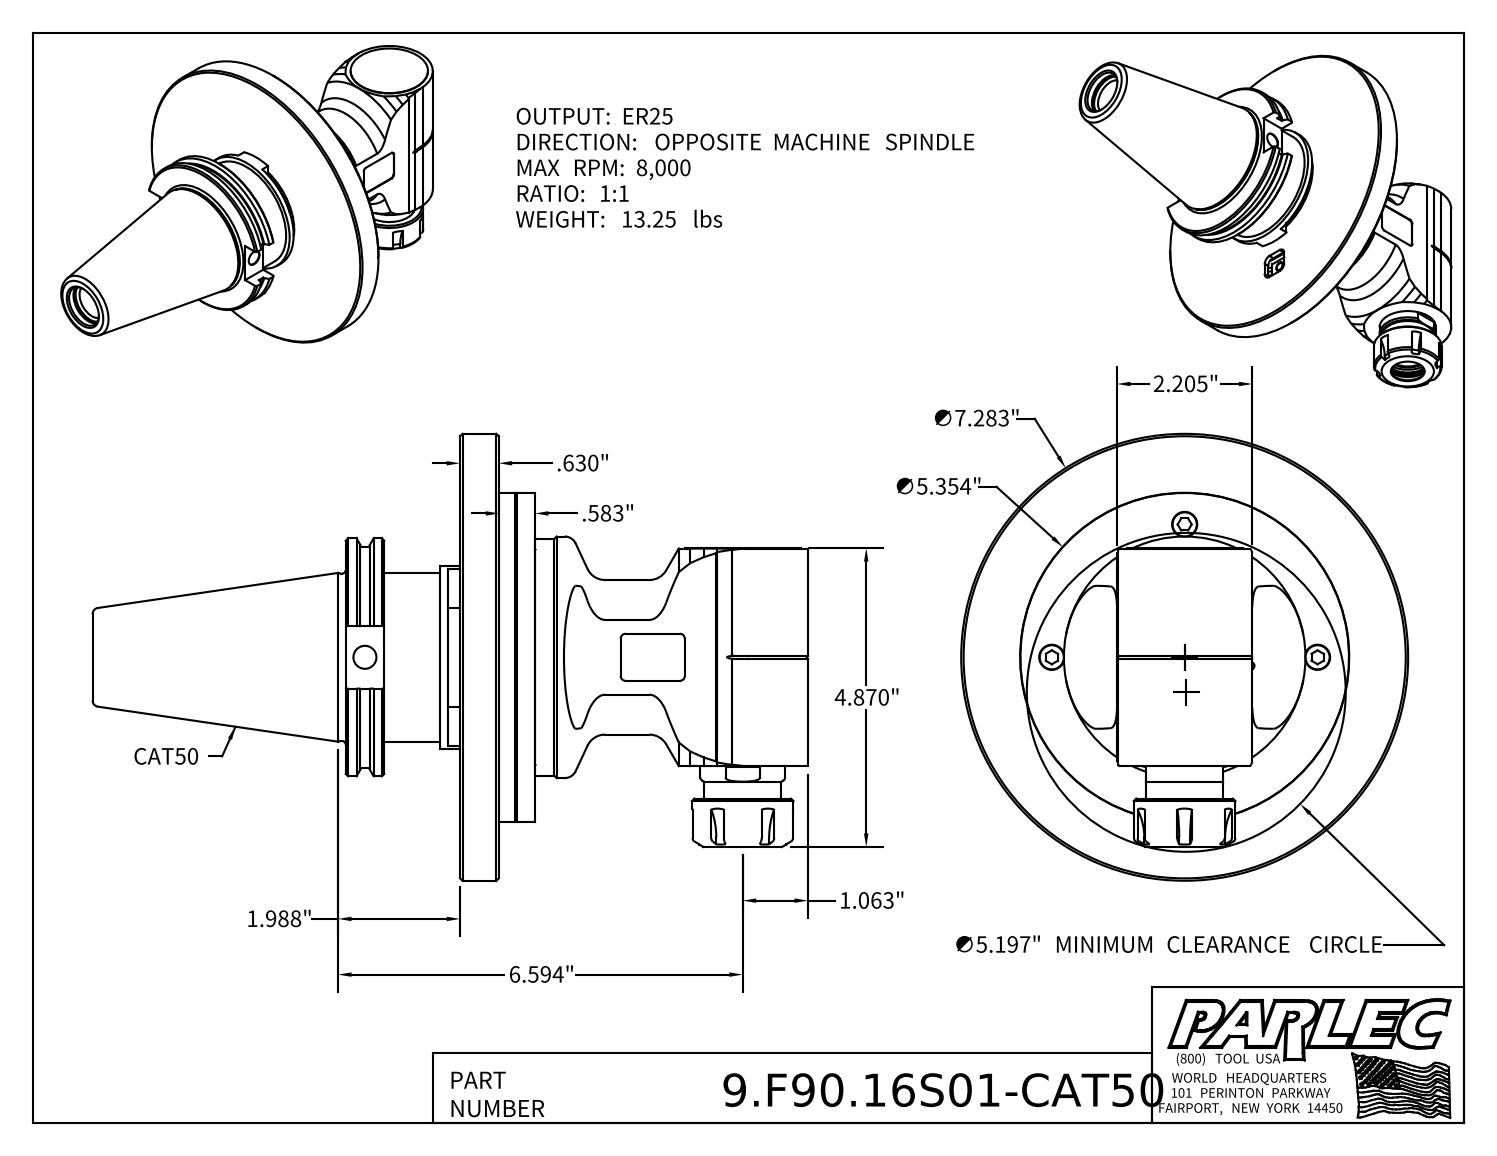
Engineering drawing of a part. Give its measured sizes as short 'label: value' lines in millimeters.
name: 9.F90.16S01-CAT50; 9_F90_16S01; 9_SK_45_2 (Cat50, MTC)
written by: Autodesk Inventor 2022 (AUTOMOTIVE_DESIGN)
unit: mm
bodies: 12 solids, 481 faces (247 planar, 108 cylindrical, 126 other)
size: 296.1 × 185 × 185
volume: 1 570 000 mm³; area: 226 800 mm²
holes: 8× ⌀10.4, 4× ⌀5, 4× ⌀6.4, 1× ⌀8.5, 1× ⌀9.5, 1× ⌀18, 1× ⌀20, 1× ⌀21, 1× ⌀22, 1× ⌀23, 1× ⌀26.2, 1× ⌀26.8
bosses: 8× ⌀10, 8× ⌀6, 2× ⌀2.5, 1× ⌀185, 1× ⌀136.2, 1× ⌀136, 1× ⌀126, 1× ⌀101.4
rounds: 12× R2, 6× R4, 6× R25, 2× R0.4, 1× R23, 1× R27, 1× R32
face distances: 16, 15, 31, 13, 3, 28, 21, 8, 5.5, 5
hole spacings: 38.9, 86.2, 38, 53.7, 55, 77.8, 76, 110
